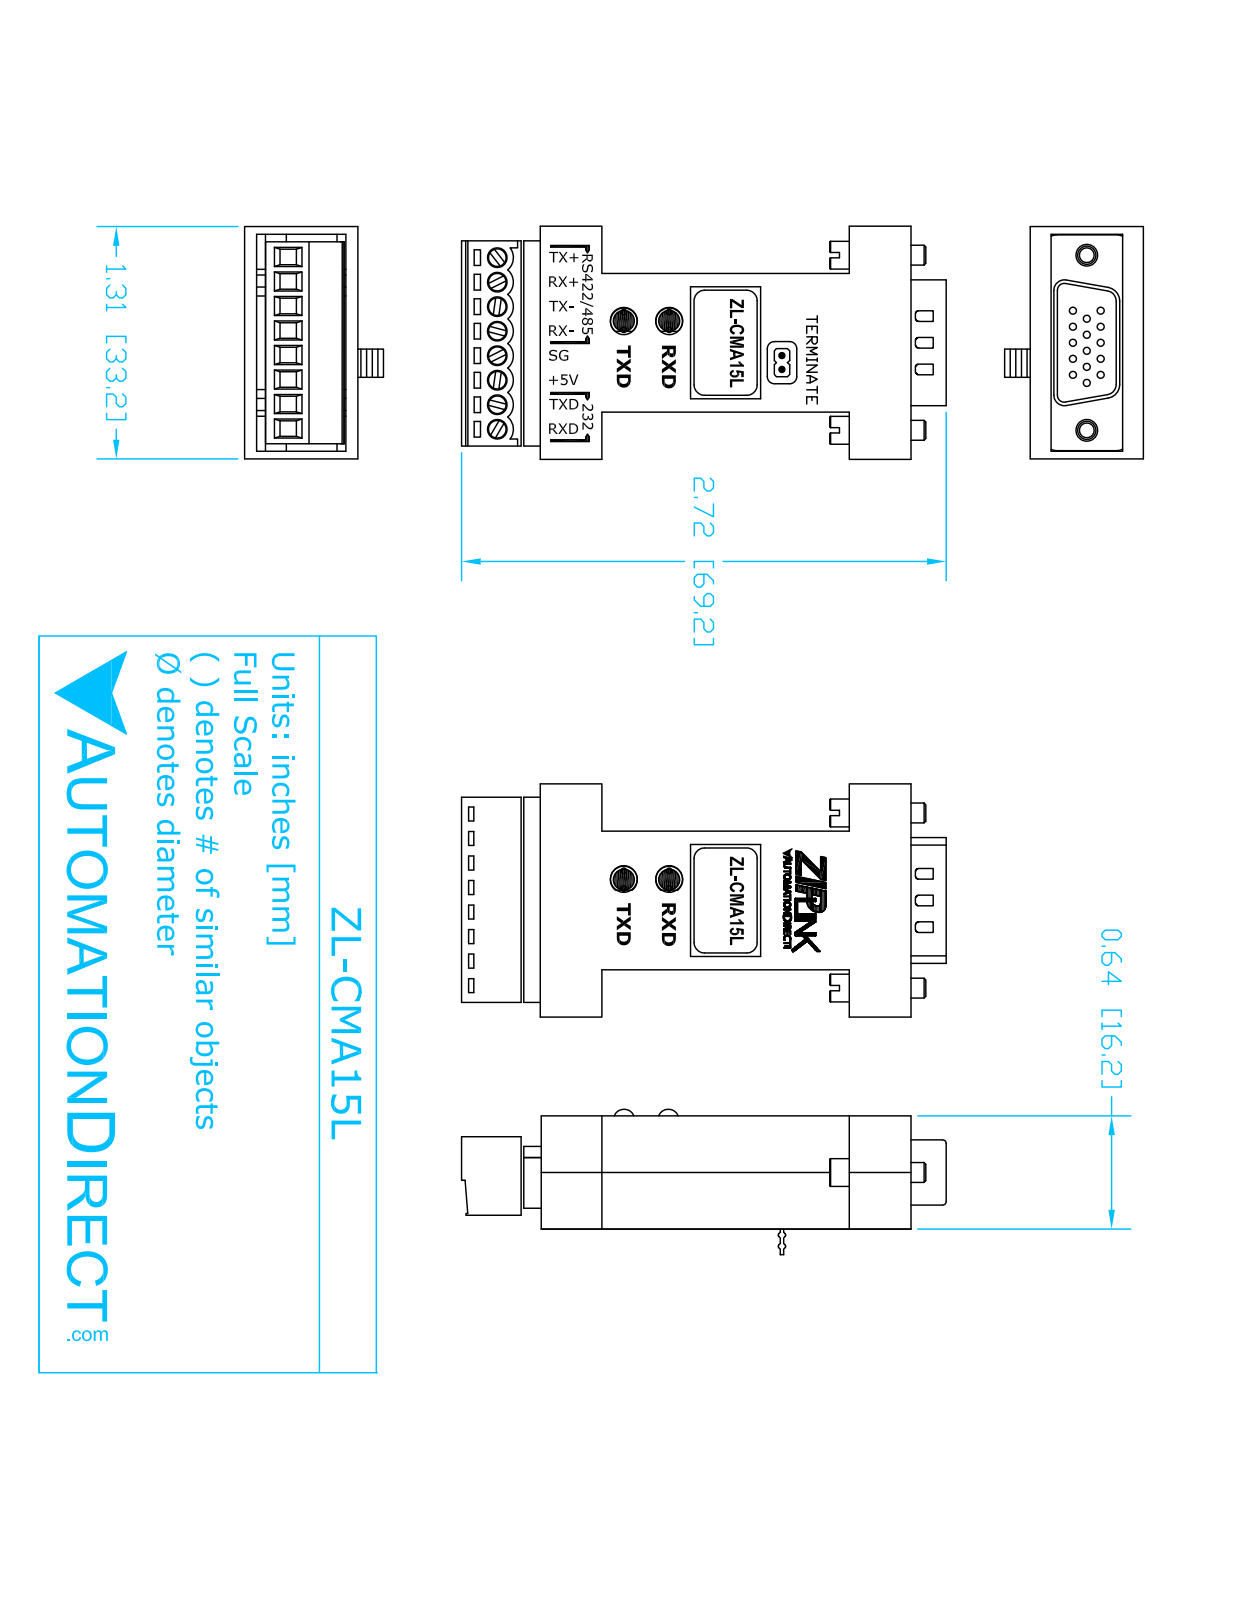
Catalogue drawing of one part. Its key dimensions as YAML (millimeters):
part_name: "ZL-CMA15L"
step_written_by: "SolidWorks 2014 (AUTOMOTIVE_DESIGN)"
units: millimeters
bodies: {solids: 1, faces: 311, planar: 208, cylindrical: 85, other: 18}
overall_size: [69.8, 33.3, 19.8]
volume: 25190
surface_area: 7684
round_holes:
  - {diameter: 1, count: 15}
  - {diameter: 2.5, count: 8}
round_bosses_or_shafts:
  - {diameter: 4.1, count: 2}
  - {diameter: 2.8, count: 2}
partial_cylinders:
  - {radius: 0.5, count: 7}
  - {radius: 1.5, count: 4}
  - {radius: 1, count: 2}
  - {radius: 2, count: 2}
face_to_face_distances: [16.3, 6.9, 26.4, 19.6, 2.5, 44.5, 9.1, 13.7, 33.3, 2]
hole_center_spacings: [2.3, 4, 4.6, 4.6, 2.3, 2.3, 6.1, 8.3]
